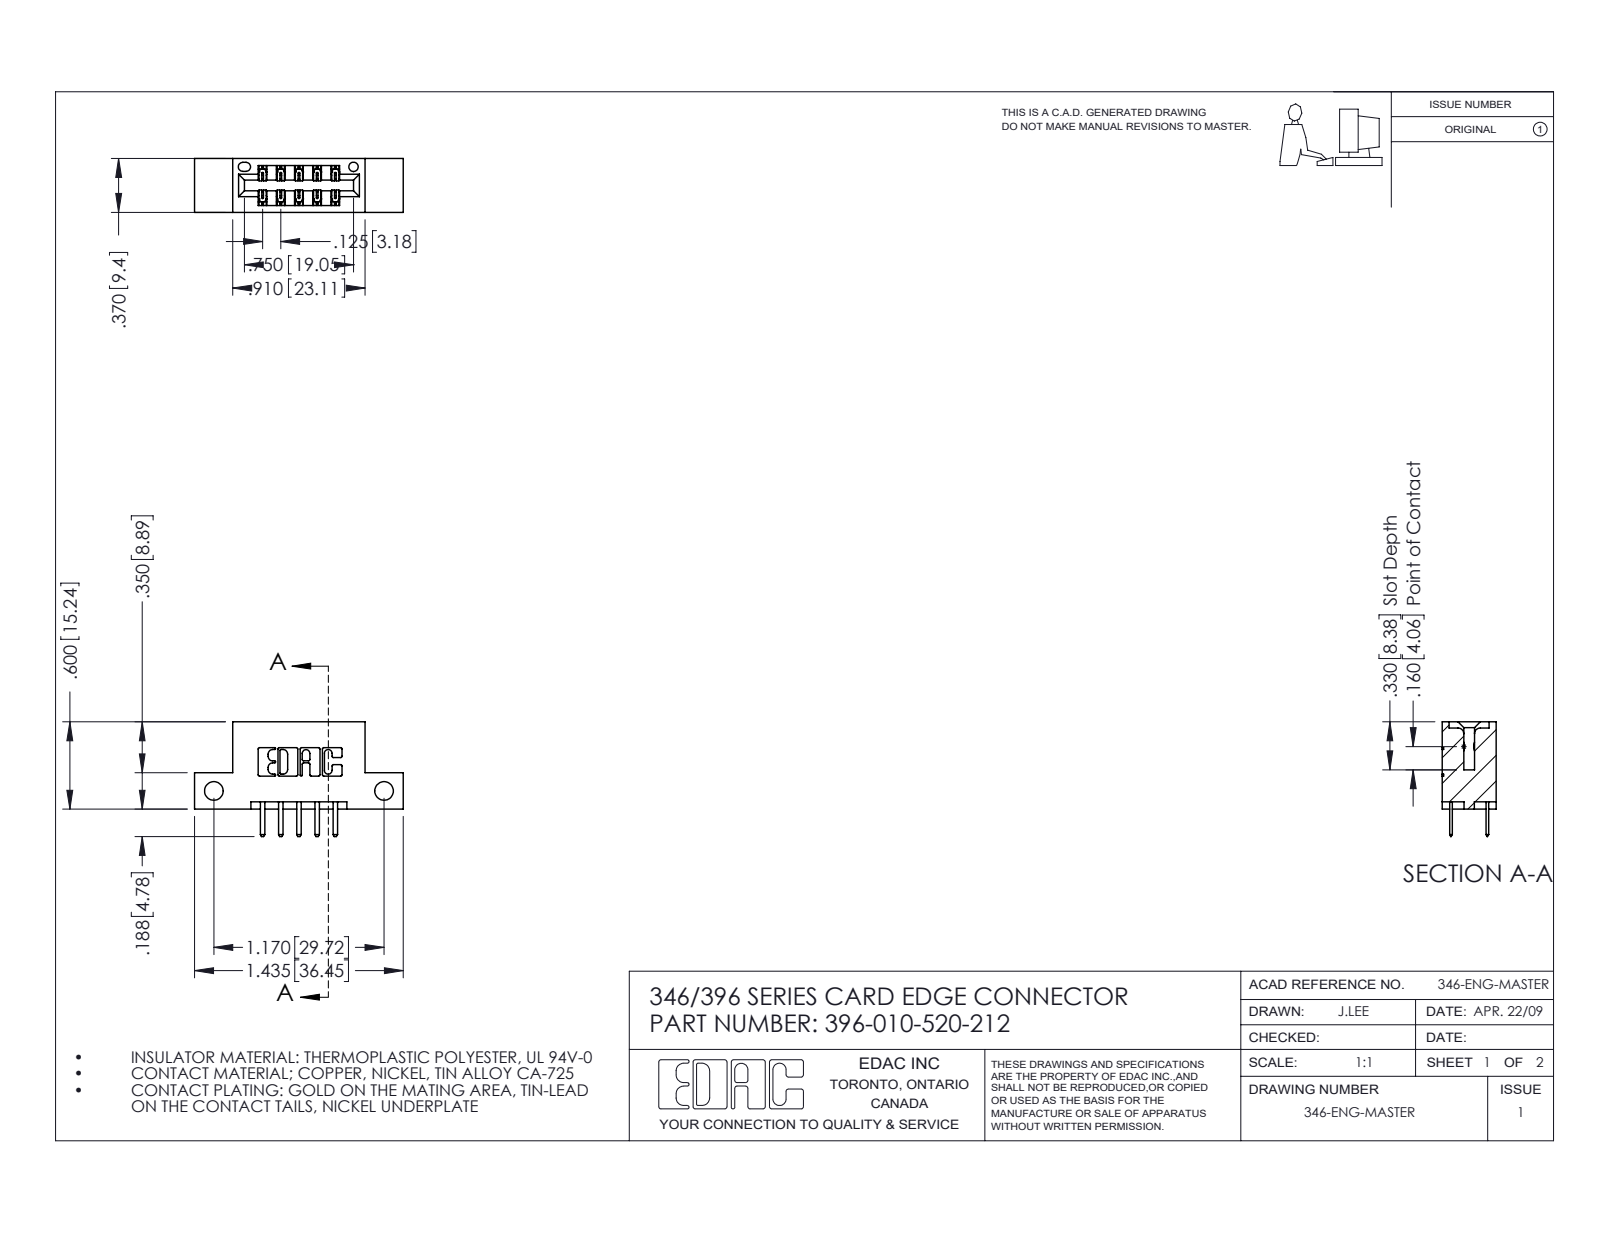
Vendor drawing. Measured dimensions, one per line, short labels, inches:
name: 345-292-001_345-293-120; 396-010-520-212; 346 Part_Flush Mounting Lugs - Side Mount
written by: SolidWorks 2016 (CONFIG_CONTROL_DESIGN)
unit: in
bodies: 11 solids, 682 faces (446 planar, 236 cylindrical, 0 other)
size: 1.435 × 0.788 × 0.37
volume: 0.194 in³; area: 5.635 in²
holes: 2× ⌀0.128, 1× ⌀0.064
rounds: 22× R0.01, 15× R0.006, 14× R0.01, 6× R0.007, 6× R0.031, 3× R0.026, 2× R0.014, 2× R0.022
face distances: 0.25, 0.37, 0.048, 0.322, 0.148, 0.222, 0.1, 0.174, 0.125, 0.275
hole spacings: 1.17
